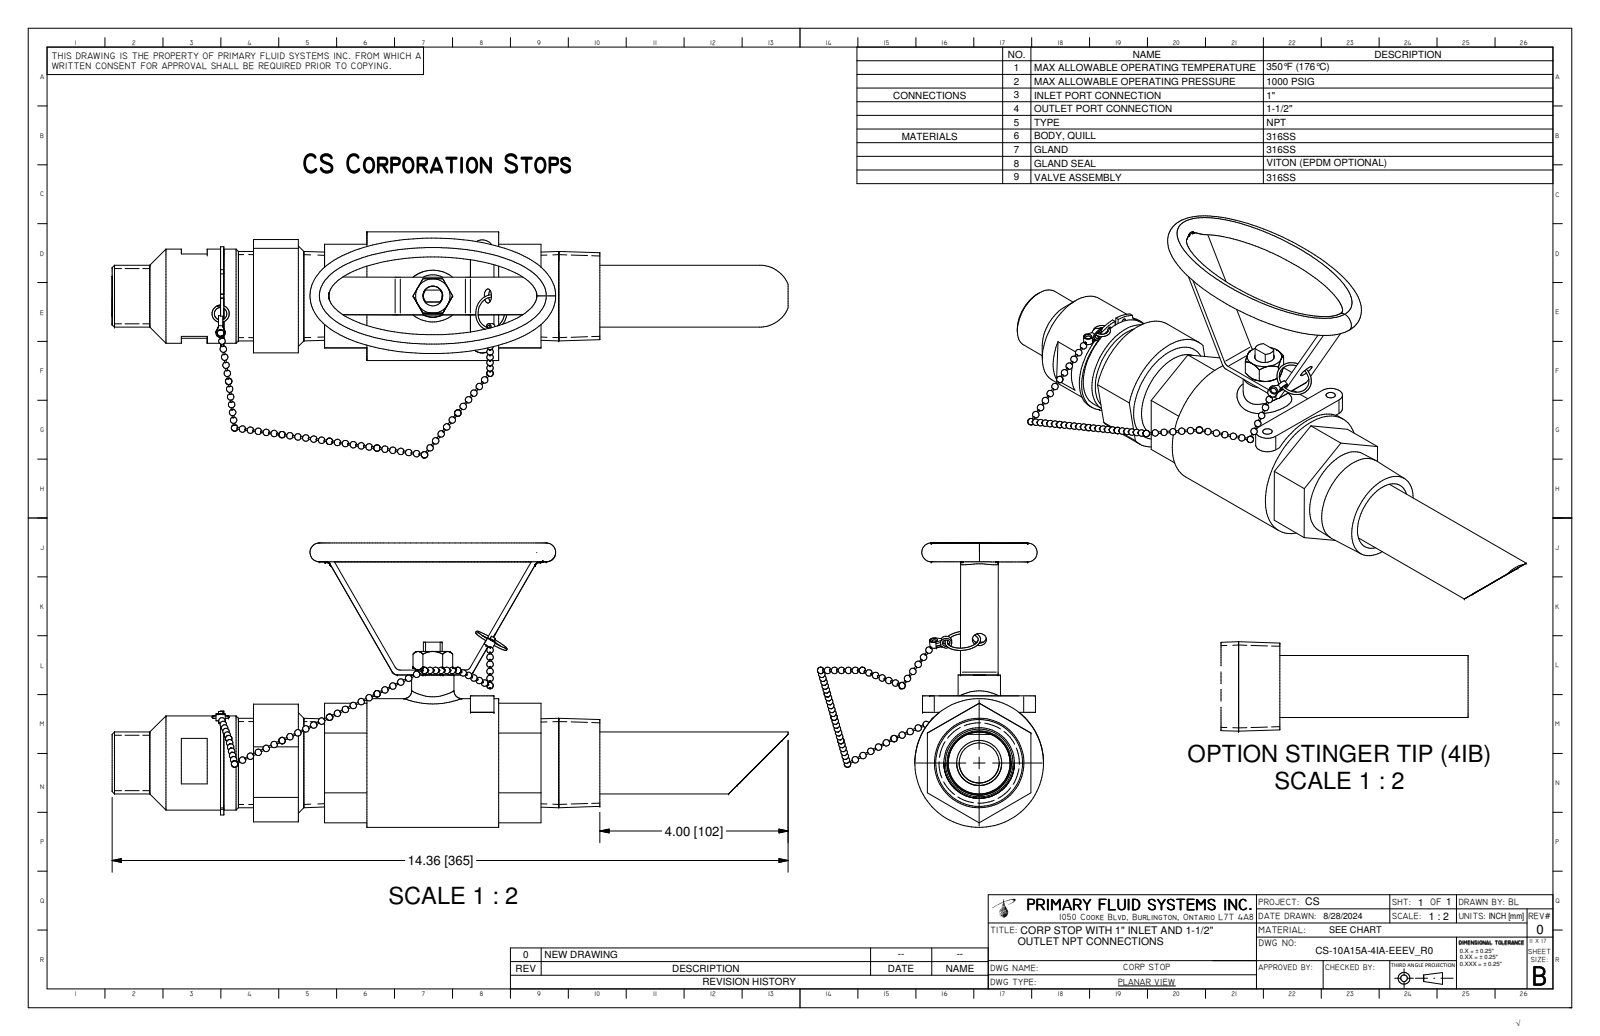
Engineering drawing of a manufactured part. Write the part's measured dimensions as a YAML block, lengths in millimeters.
step_written_by: "Autodesk Inventor 2025 (CONFIG_CONTROL_DESIGN)"
units: millimeters
bodies: {solids: 21, faces: 333, planar: 125, cylindrical: 111, other: 97}
overall_size: [364.8, 153.4, 122]
volume: 579900
surface_area: 177600
round_holes:
  - {diameter: 1.7, count: 2}
  - {diameter: 2.5, count: 2}
  - {diameter: 3.8, count: 2}
  - {diameter: 4, count: 2}
  - {diameter: 5.1, count: 2}
  - {diameter: 7.6, count: 1}
  - {diameter: 10.7, count: 1}
  - {diameter: 21.6, count: 1}
  - {diameter: 24.3, count: 1}
  - {diameter: 34.7, count: 1}
  - {diameter: 38.1, count: 1}
  - {diameter: 44, count: 1}
round_bosses_or_shafts:
  - {diameter: 0.9, count: 9}
  - {diameter: 6, count: 2}
  - {diameter: 69.4, count: 1}
  - {diameter: 50.8, count: 1}
  - {diameter: 45.7, count: 1}
  - {diameter: 41.8, count: 1}
  - {diameter: 37.7, count: 1}
  - {diameter: 33.4, count: 1}
partial_cylinders:
  - {radius: 3.2, count: 6}
  - {radius: 1.2, count: 2}
  - {radius: 2.5, count: 2}
  - {radius: 5, count: 2}
  - {radius: 6.4, count: 2}
  - {radius: 5.1, count: 1}
  - {radius: 26.6, count: 1}
  - {radius: 28, count: 1}
face_to_face_distances: [2.6, 22.9, 94, 55.9, 55.9, 55.9, 116.8, 71.1, 38.3, 61.2]
hole_center_spacings: [25.5, 8, 11, 18, 19, 28.2, 35.8, 36.1]
